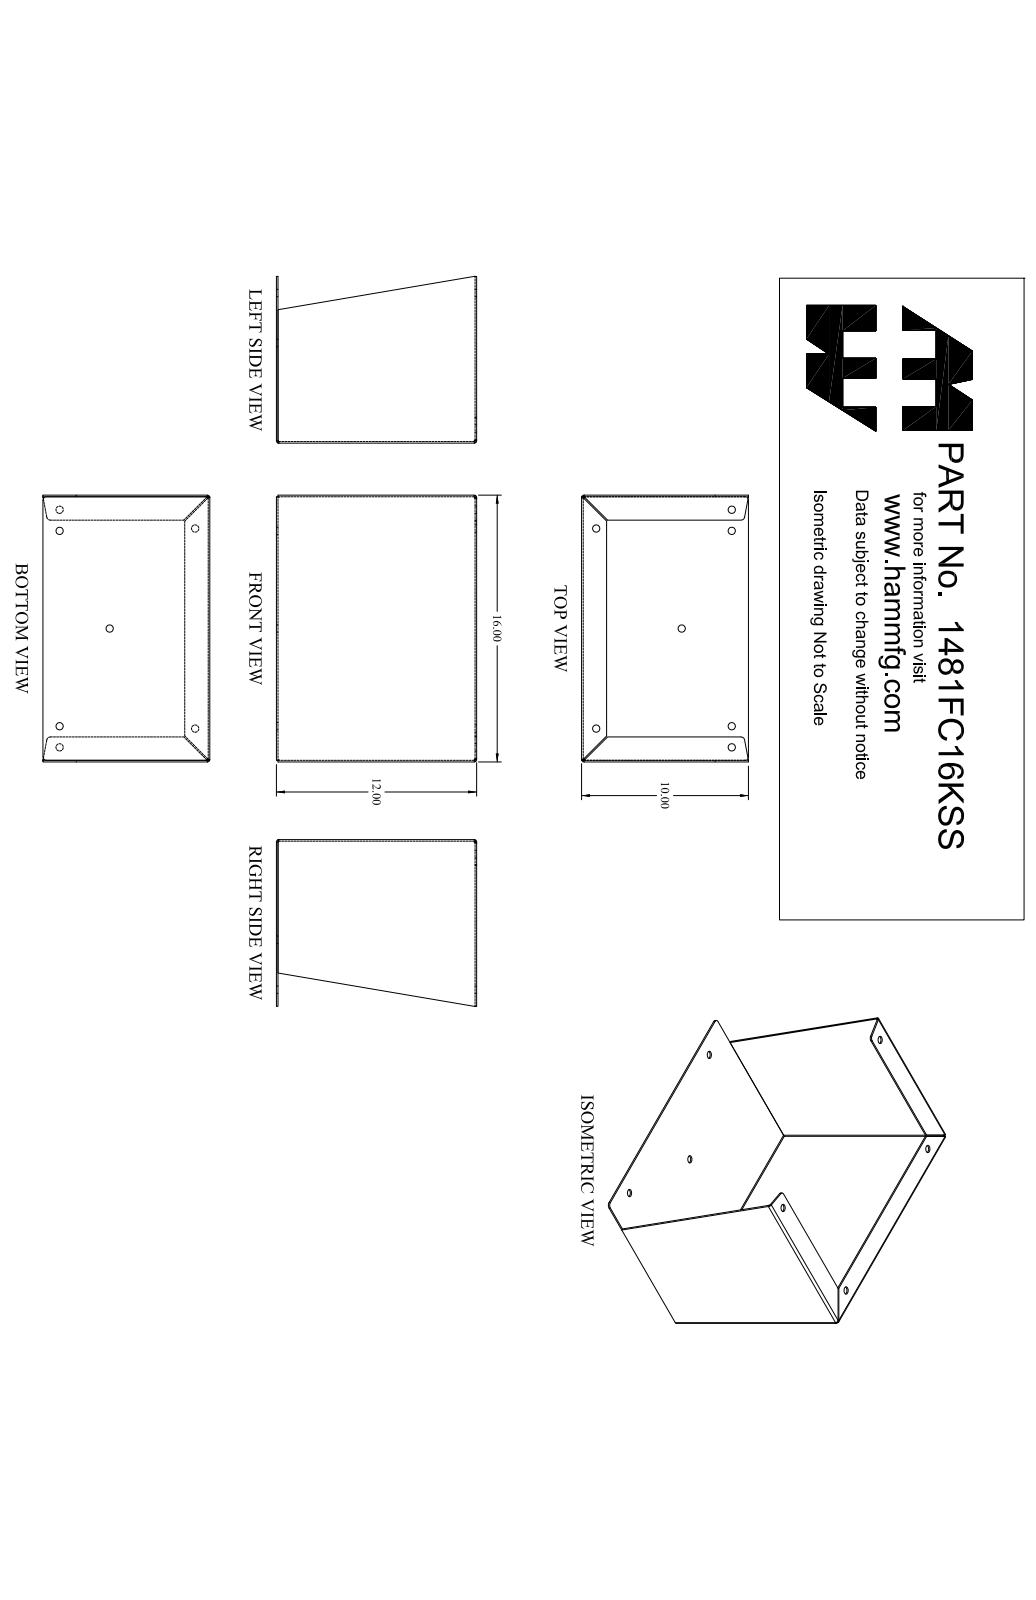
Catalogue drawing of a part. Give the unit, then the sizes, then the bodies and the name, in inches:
Units: inches
Overall size (bounding box): 16 × 12 × 10
Round holes (diameter × count): ⌀0.437 ×7
Partial cylindrical surfaces — rounded edges, fillets, slot ends (radius × count): R0.048 ×6, R0.143 ×6, R0.22 ×4
Main face-to-face distances: 0.095, 15.905, 0.095, 16, 15.81, 11.81, 11.905, 11.905, 12, 1.405
Hole centre spacings: 6.582, 7.891, 8.126, 8.202, 14.375, 1.266, 1.266, 7.731
Volume: 57.2 in³ · Surface area: 1 216 in²
Bodies: 1 solid, 78 faces (42 planar, 30 cylindrical, 6 other)
Part name (STEP PRODUCT): 1481FC16KSS_Default
STEP written by: SolidWorks 2019 (CONFIG_CONTROL_DESIGN)
